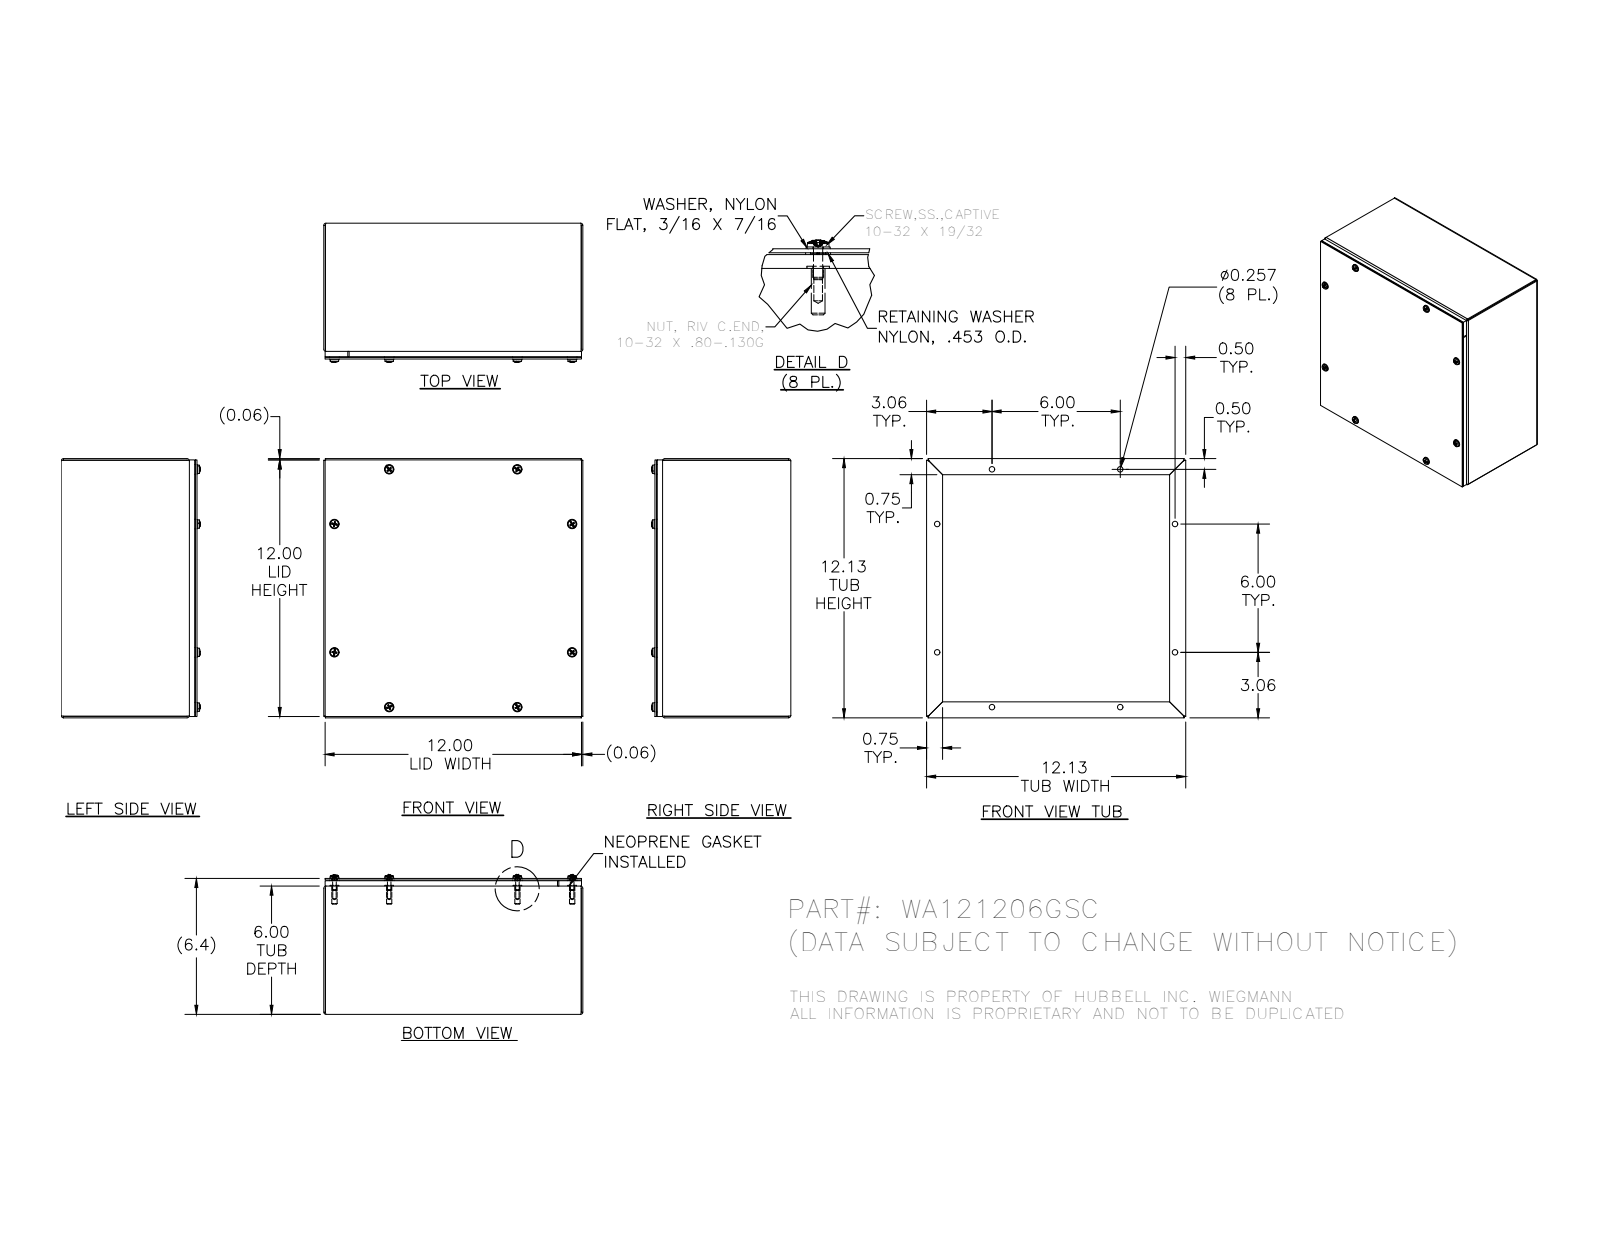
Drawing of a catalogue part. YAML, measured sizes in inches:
part_name: "WA121206GSC; 316282; WA121206GSCBKP; WA1212GSC_LP (+4 more)"
step_written_by: "SolidWorks 2014 (AUTOMOTIVE_DESIGN)"
units: inches
bodies: {solids: 36, faces: 892, planar: 420, cylindrical: 240, other: 232}
overall_size: [12.125, 12.125, 6.511]
volume: 54.63
surface_area: 1339
round_holes:
  - {diameter: 0.156, count: 8}
  - {diameter: 0.188, count: 8}
  - {diameter: 0.196, count: 8}
  - {diameter: 0.257, count: 8}
  - {diameter: 0.278, count: 8}
  - {diameter: 0.281, count: 8}
  - {diameter: 0.313, count: 8}
round_bosses_or_shafts:
  - {diameter: 0.453, count: 8}
  - {diameter: 0.437, count: 8}
  - {diameter: 0.406, count: 8}
  - {diameter: 0.248, count: 8}
  - {diameter: 0.167, count: 8}
partial_cylinders:
  - {radius: 0.031, count: 8}
  - {radius: 0.089, count: 8}
  - {radius: 0.105, count: 8}
face_to_face_distances: [0.074, 6.282, 12.051, 6.356, 6.208, 12.125, 11.977, 0.356, 5.926, 0.282]
hole_center_spacings: [6, 8.938, 8.937, 3.624, 8.937, 12.109, 11.124, 11.125]
